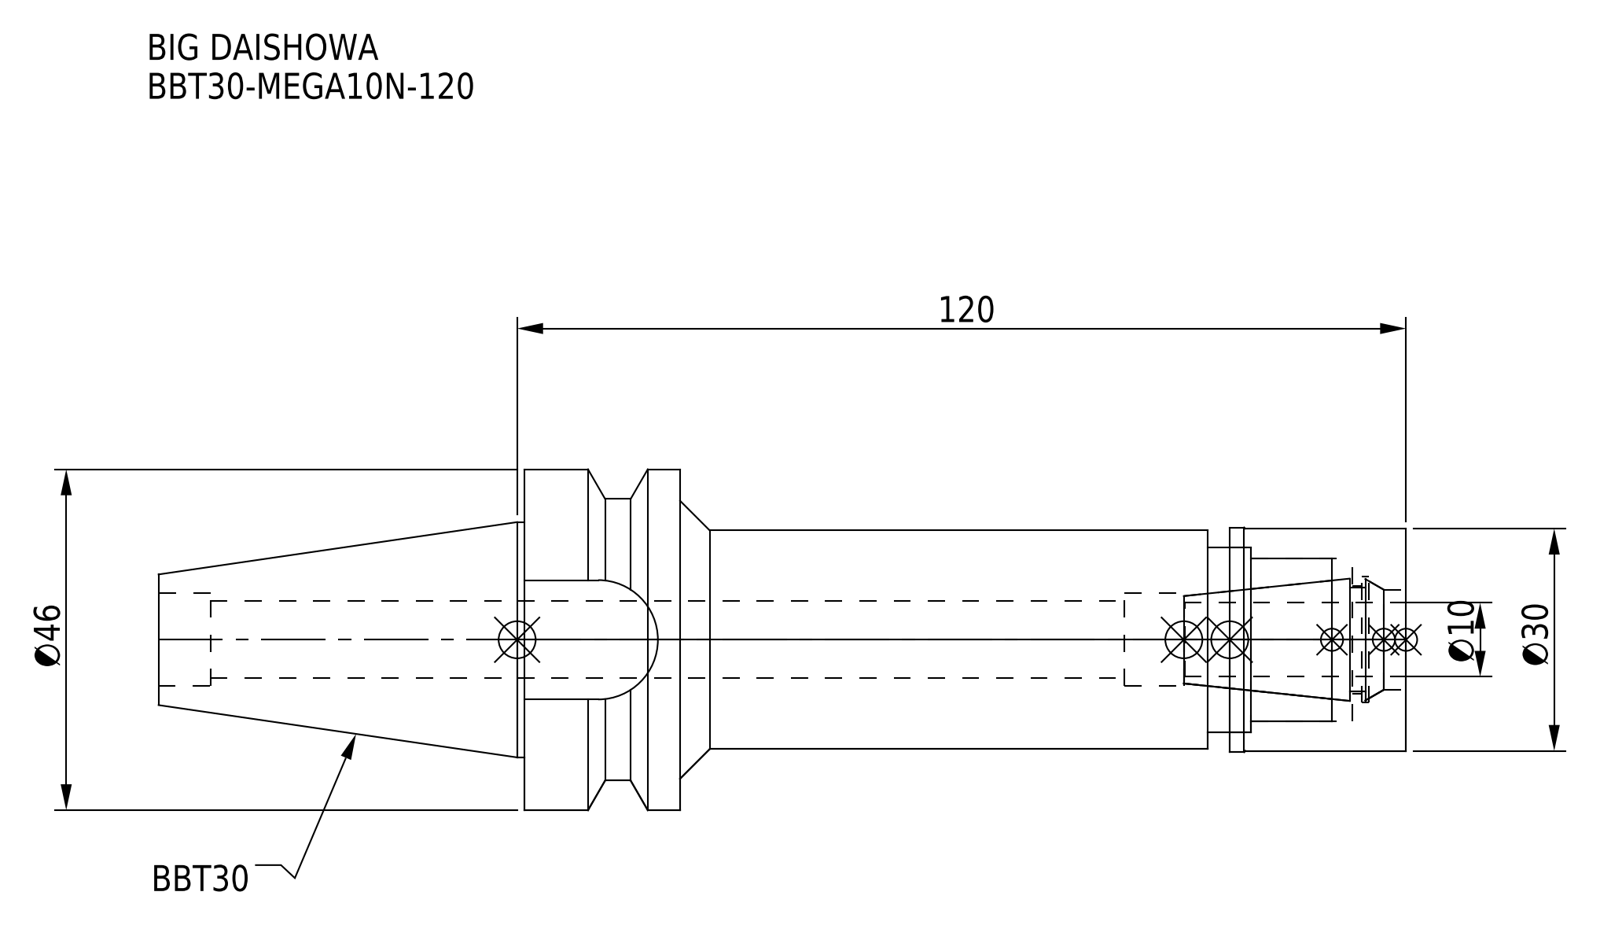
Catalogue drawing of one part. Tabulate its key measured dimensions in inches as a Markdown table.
| quantity | value |
| --- | --- |
| part name | BBT30-MEGA10N-120-100.stp; BBT30-MEGA10N-120_1.stp; BBT30-MEGA10N-120; MGN10_1.stp (+3 more) |
| STEP written by | SolidWorks 2019 (CONFIG_CONTROL_DESIGN) |
| units | inches |
| bodies | 2 solids, 73 faces (21 planar, 38 cylindrical, 14 other) |
| overall size | 6.63 × 1.811 × 1.811 |
| volume | 6.347 in³ |
| surface area | 43.54 in² |
| round holes (diameter × count) | 0.409 × 1, 0.492 × 1, 0.531 × 1, 0.571 × 1, 0.669 × 1, 0.866 × 1, 0.984 × 1 |
| round bosses / shafts (diameter × count) | 1.811 × 1, 1.25 × 1, 1.193 × 1, 1.181 × 1, 1.161 × 1 |
| partial cylindrical surfaces (radius × count) | 0.317 × 1, 0.748 × 1 |
| main face-to-face distances | 4.685, 3.858, 0.827, 1.283, 0.937, 2.921, 3.748, 0.823, 0.114, 3.035 |
